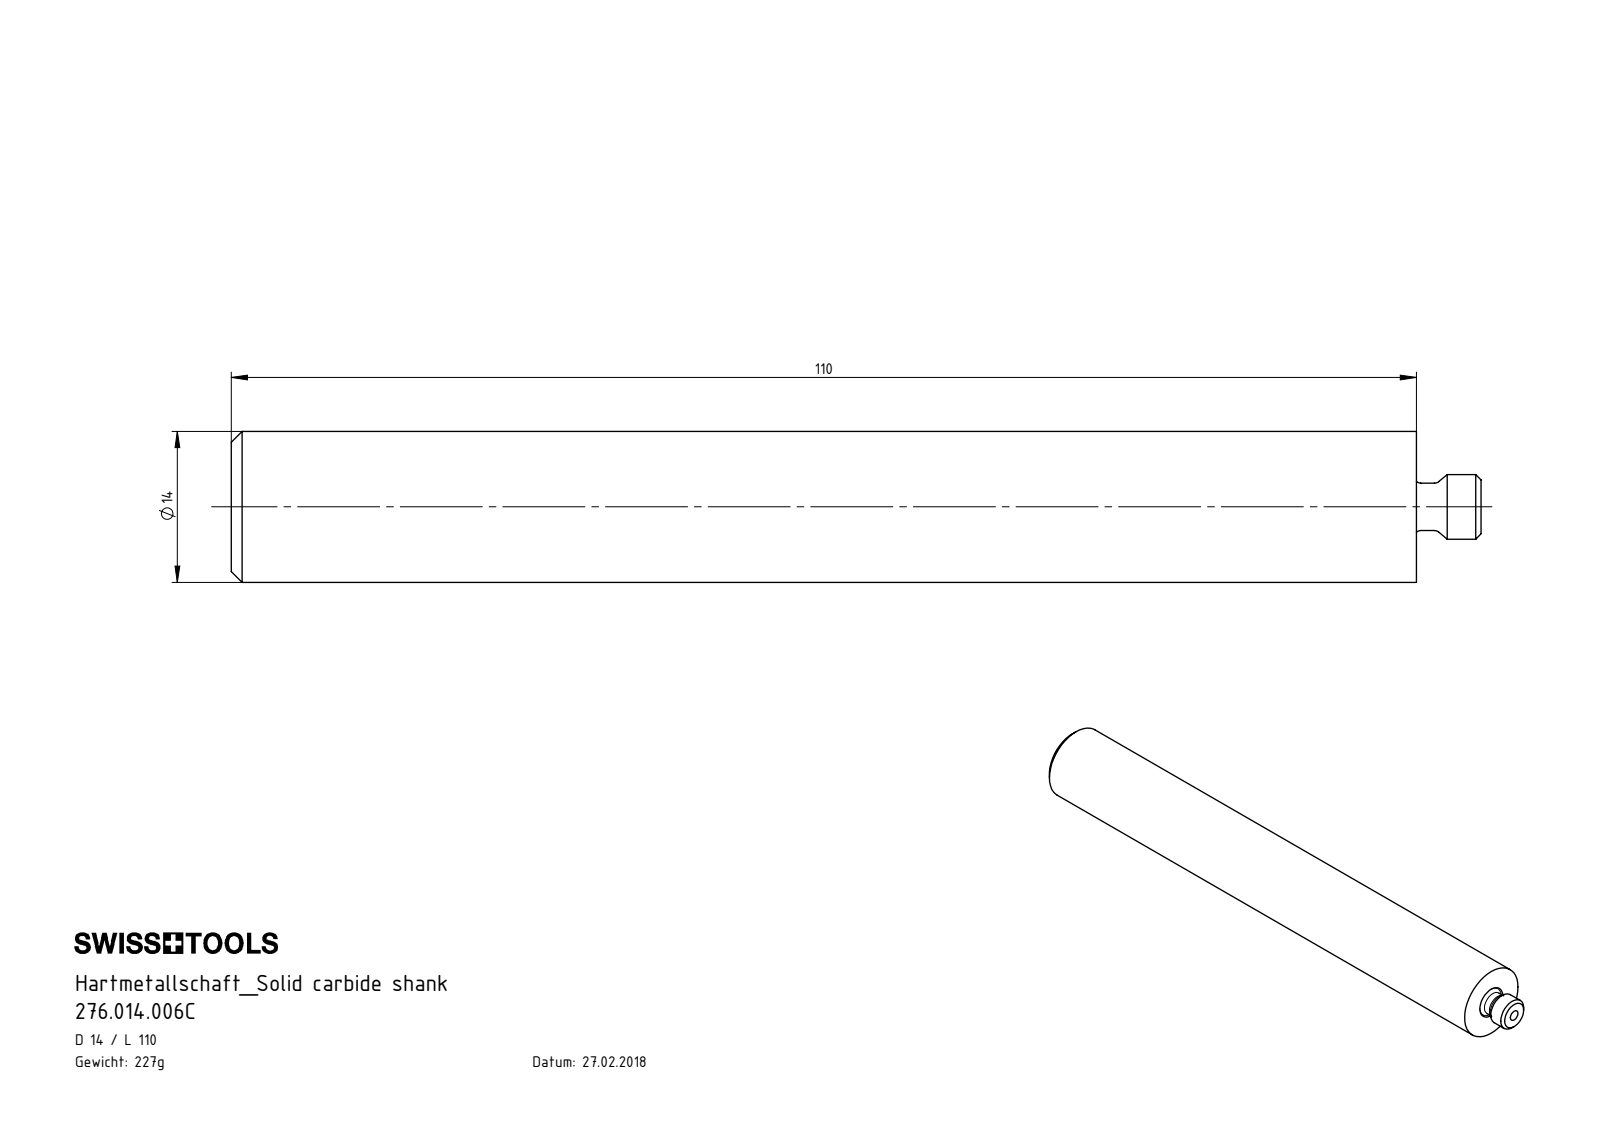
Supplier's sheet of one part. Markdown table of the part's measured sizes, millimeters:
| quantity | value |
| --- | --- |
| part name | HM1-BG1.006.015_A; HM1-U14.001.110_A; 276.014.006C |
| STEP written by | SolidWorks 2017 (CONFIG_CONTROL_DESIGN) |
| units | millimeters |
| bodies | 2 solids, 35 faces (5 planar, 14 cylindrical, 16 other) |
| overall size | 116 × 14 × 14 |
| volume | 15 787 mm³ |
| surface area | 6 929 mm² |
| round holes (diameter × count) | 2 × 1, 4 × 1, 5 × 1 |
| round bosses / shafts (diameter × count) | 14 × 1, 6 × 1, 4.4 × 1 |
| main face-to-face distances | 110, 100.8, 116, 9.2, 15.2, 6, 109.8, 9, 6.2 |
